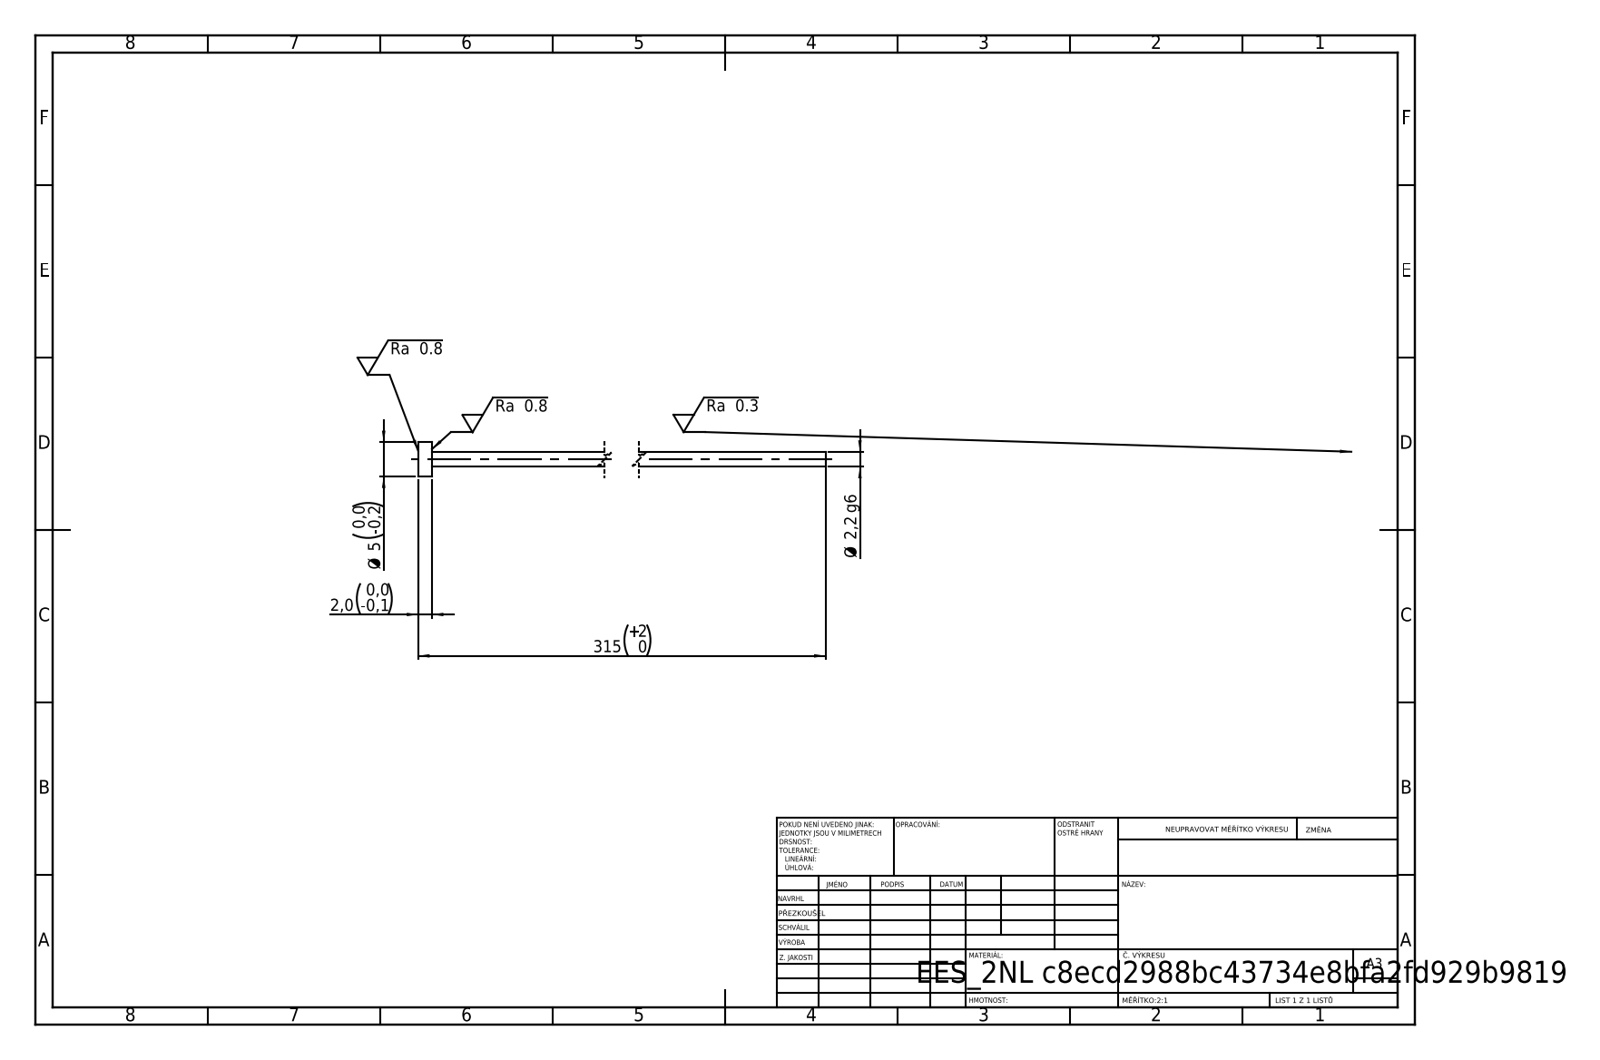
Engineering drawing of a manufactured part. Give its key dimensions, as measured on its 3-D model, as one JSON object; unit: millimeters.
{"step_written_by": "SolidWorks 2019 (CONFIG_CONTROL_DESIGN)", "units": "millimeters", "bodies": {"solids": 1, "faces": 7, "planar": 3, "cylindrical": 4, "other": 0}, "overall_size": [315, 5, 5], "volume_mm3": 1229, "surface_area_mm2": 2234, "round_bosses_or_shafts": [[5, 1], [2.2, 1]], "face_to_face_distances": [2, 315, 313]}
